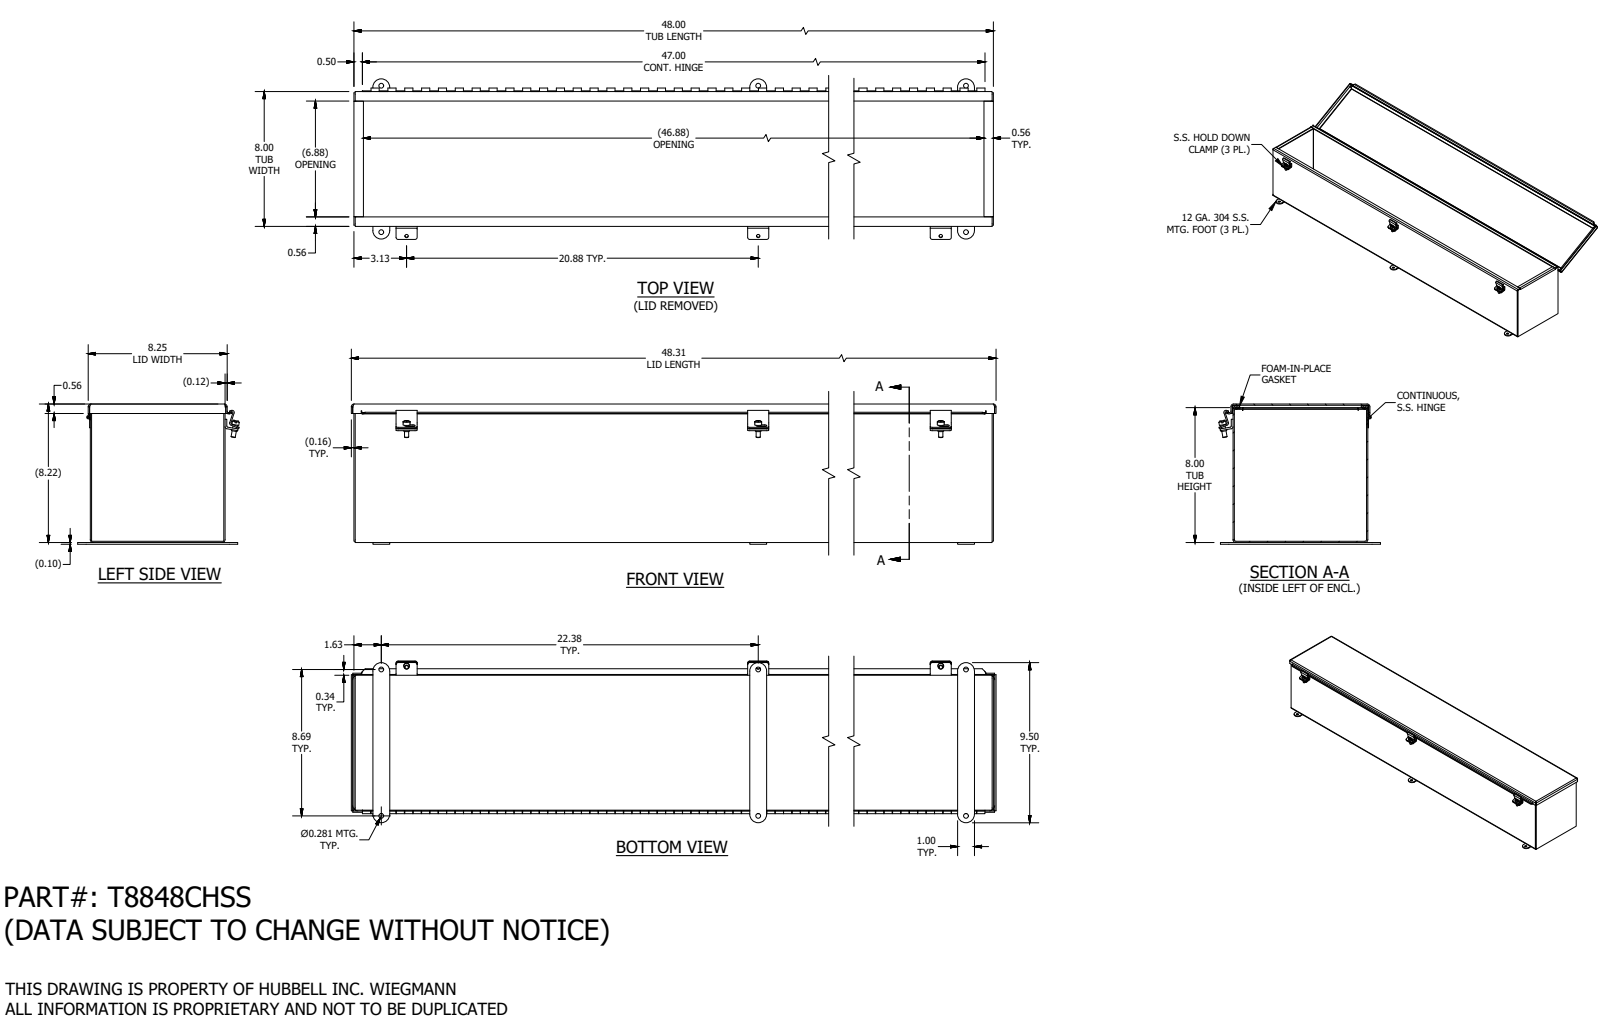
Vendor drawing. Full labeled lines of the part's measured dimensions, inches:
Part name (STEP PRODUCT): T8848CHSS
STEP written by: SolidWorks 2019 (AUTOMOTIVE_DESIGN)
Units: inches
Bodies: 20 solids, 839 faces (503 planar, 297 cylindrical, 39 other)
Overall size (bounding box): 48.313 × 9.598 × 8.322
Volume: 147.8 in³ · Surface area: 3 947 in²
Round holes (diameter × count): ⌀0.11 ×6, ⌀0.281 ×6, ⌀0.196 ×3, ⌀0.116 ×1
Round bosses / shafts (diameter × count): ⌀0.41 ×3, ⌀0.344 ×3, ⌀0.25 ×3, ⌀0.2 ×1, ⌀0.1 ×1
Partial cylindrical surfaces — rounded edges, fillets, slot ends (radius × count): R0.125 ×12, R0.094 ×11, R0.168 ×11, R0.085 ×8, R0.133 ×6, R0.5 ×6, R0.242 ×4, R0.063 ×3
Main face-to-face distances: 0.074, 7.926, 8.144, 8, 7.852, 8.218, 8.07, 47.926, 0.218, 8.052
Hole centre spacings: 20.875, 22.375, 24.002, 0.75, 8.687, 20.875, 41.75, 44.75
